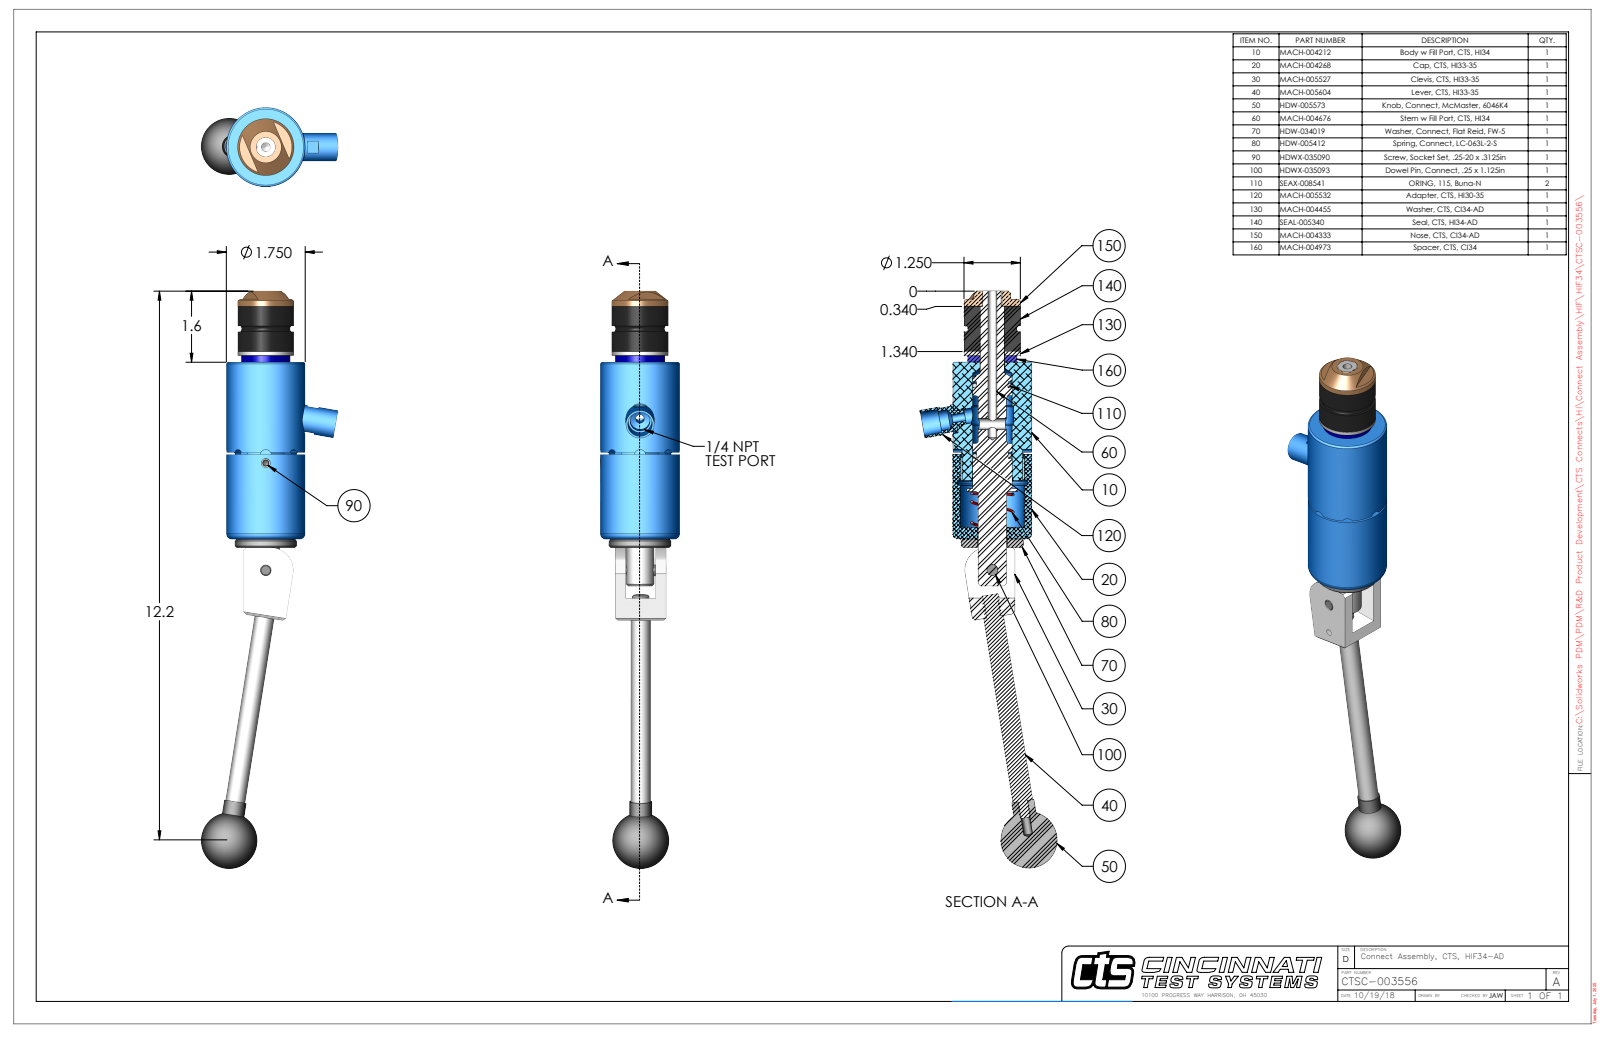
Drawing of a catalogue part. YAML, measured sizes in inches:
part_name: "CTSC-003556"
step_written_by: "SolidWorks 2023 (AUTOMOTIVE_DESIGN)"
units: inches
bodies: {solids: 10, faces: 290, planar: 105, cylindrical: 120, other: 65}
overall_size: [12.795, 3.043, 1.75]
volume: 14.31
surface_area: 81.58
round_holes:
  - {diameter: 0.201, count: 2}
  - {diameter: 0.15, count: 1}
  - {diameter: 0.187, count: 1}
  - {diameter: 0.204, count: 1}
  - {diameter: 0.249, count: 1}
  - {diameter: 0.25, count: 1}
  - {diameter: 0.251, count: 1}
  - {diameter: 0.313, count: 1}
  - {diameter: 0.422, count: 1}
  - {diameter: 0.438, count: 1}
  - {diameter: 0.53, count: 1}
  - {diameter: 0.541, count: 1}
round_bosses_or_shafts:
  - {diameter: 0.5, count: 2}
  - {diameter: 0.44, count: 2}
  - {diameter: 0.25, count: 2}
  - {diameter: 1.75, count: 1}
  - {diameter: 1.38, count: 1}
  - {diameter: 1.25, count: 1}
  - {diameter: 1.09, count: 1}
  - {diameter: 0.625, count: 1}
partial_cylinders:
  - {radius: 0.125, count: 4}
  - {radius: 0.029, count: 2}
  - {radius: 0.178, count: 1}
  - {radius: 0.33, count: 1}
  - {radius: 0.5, count: 1}
  - {radius: 0.695, count: 1}
  - {radius: 0.836, count: 1}
face_to_face_distances: [3.921, 1.237, 5.158, 1, 0.237, 4.158, 1.094, 0.094, 0.143, 4.064]
hole_center_spacings: [0.74, 2.376, 3.116]
